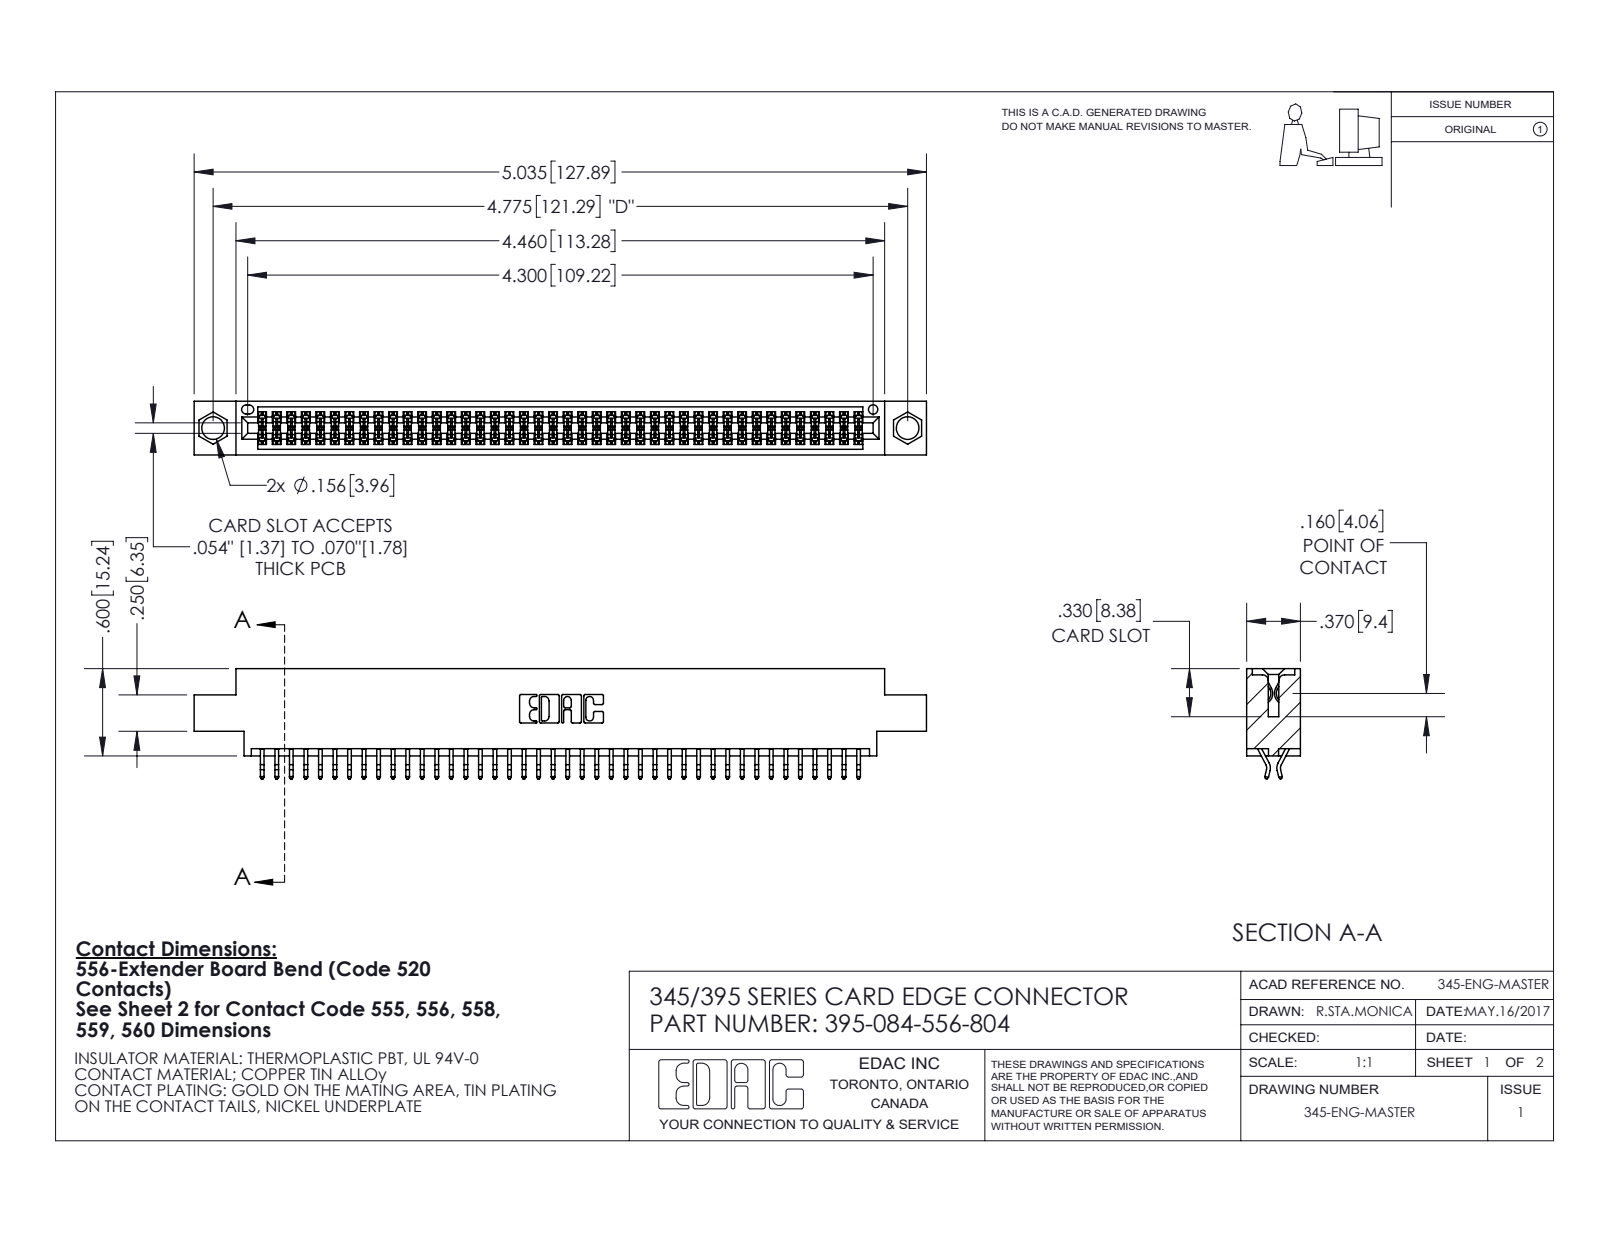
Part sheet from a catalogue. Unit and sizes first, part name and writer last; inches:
Units: inches
Overall size (bounding box): 5.035 × 0.757 × 0.37
Round holes (diameter × count): ⌀0.156 ×2, ⌀0.064 ×1
Partial cylindrical surfaces — rounded edges, fillets, slot ends (radius × count): R0.006 ×168, R0.01 ×22, R0.007 ×6, R0.031 ×6, R0.026 ×3, R0.01 ×2, R0.014 ×2, R0.019 ×2
Main face-to-face distances: 0.072, 0.298, 0.37, 0.2, 0.025, 0.098, 0.272, 0.225, 0.175, 0.149
Hole centre spacings: 0.27, 4.539, 4.775
Volume: 0.745 in³ · Surface area: 27.83 in²
Bodies: 85 solids, 4848 faces (3206 planar, 1642 cylindrical, 0 other)
Part name (STEP PRODUCT): 345-292-001_556 Tail; 345 Part_0.170 Offset - 0.156 Dia-TI; 395-084-556-804
STEP written by: SolidWorks 2020 (CONFIG_CONTROL_DESIGN)
